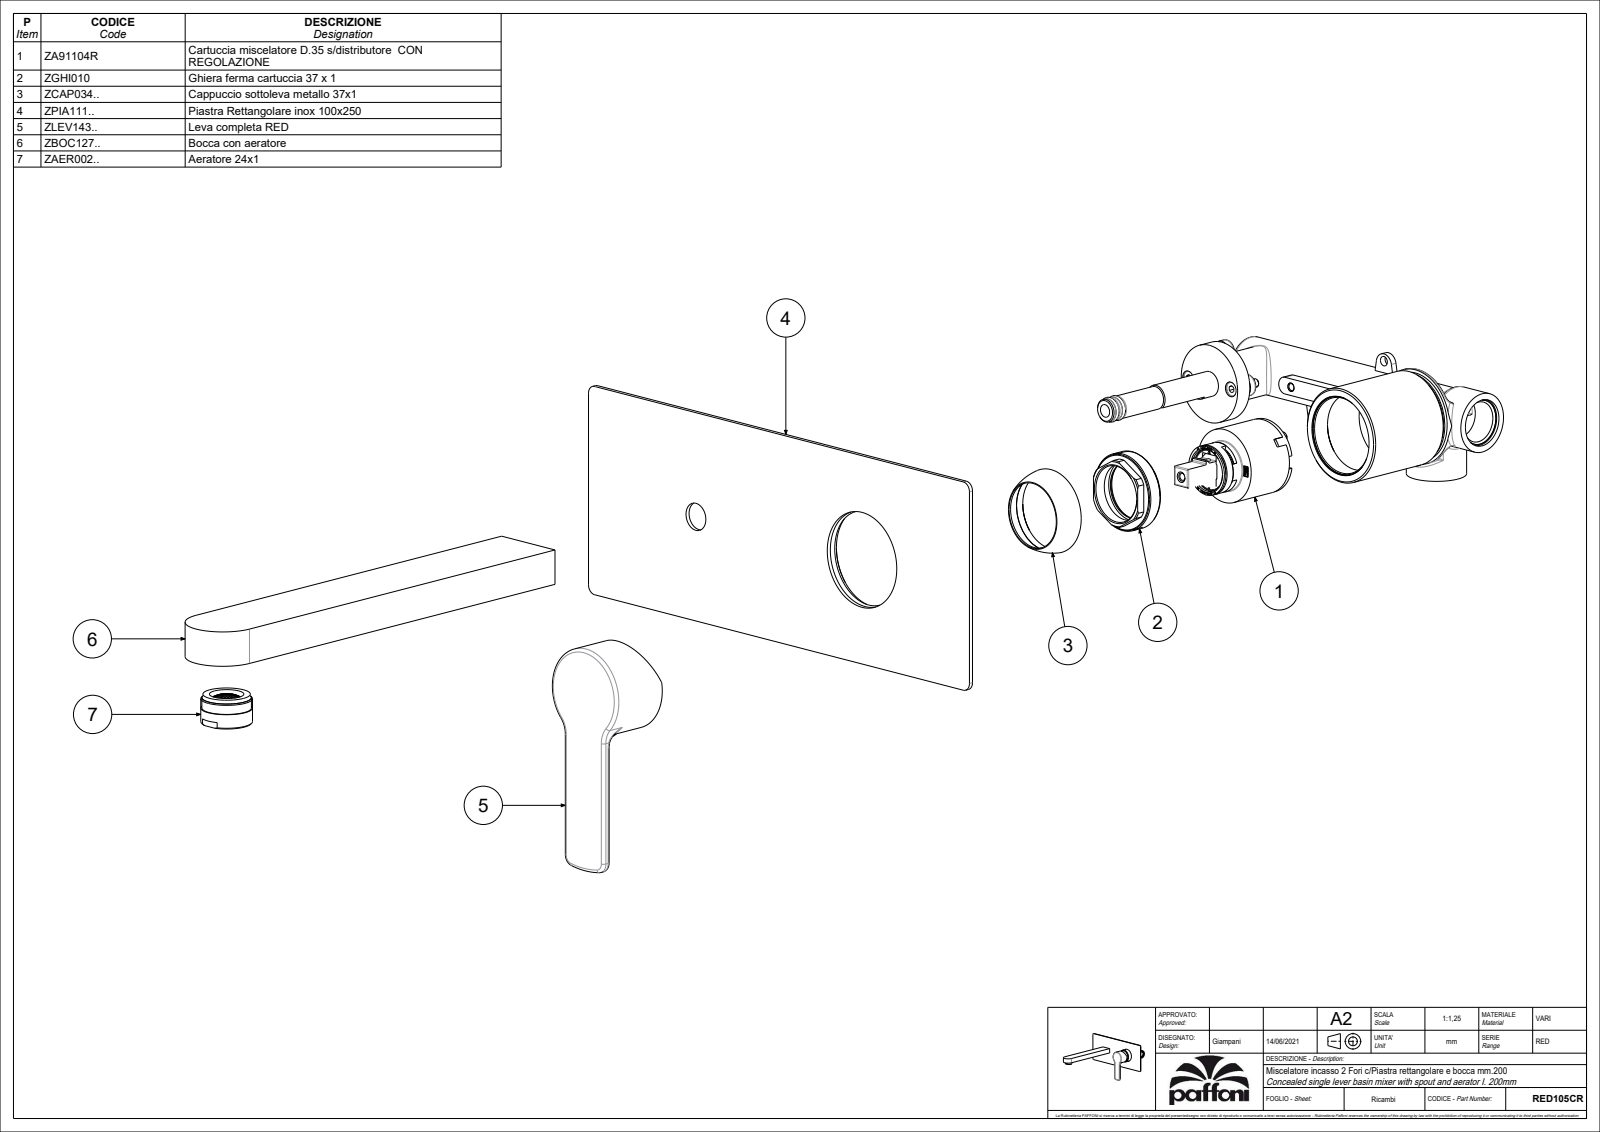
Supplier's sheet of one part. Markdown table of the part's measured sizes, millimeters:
| quantity | value |
| --- | --- |
| part name | RED105CR |
| STEP written by | CREO PARAMETRIC BY PTC INC, 2020044 (CONFIG_CONTROL_DESIGN) |
| units | millimeters |
| bodies | 4 solids, 2521 faces (2012 planar, 283 cylindrical, 226 other) |
| overall size | 250 × 220 × 135 |
| volume | 200 391 mm³ |
| surface area | 118 130 mm² |
| round holes (diameter × count) | 3.3 × 2, 4 × 2, 6 × 2, 3 × 1, 4.5 × 1, 5 × 1, 11 × 1, 12 × 1, 13 × 1, 15 × 1, 16 × 1, 17 × 1 |
| round bosses / shafts (diameter × count) | 44.8 × 1, 43 × 1, 35 × 1, 24 × 1, 23.5 × 1, 23.4 × 1, 21.8 × 1, 19.5 × 1 |
| partial cylindrical surfaces (radius × count) | 0.5 × 45, 0.15 × 11, 0.3 × 4, 1.5 × 4, 4 × 4, 1 × 2, 2.1 × 2, 2.5 × 2 |
| main face-to-face distances | 2, 16.5, 35, 50.1, 48.1, 4.5, 54.6, 52.6, 41.75, 58.25 |
| hole center spacings | 2.5, 12.5, 109, 109.03, 194.76, 205.24 |
